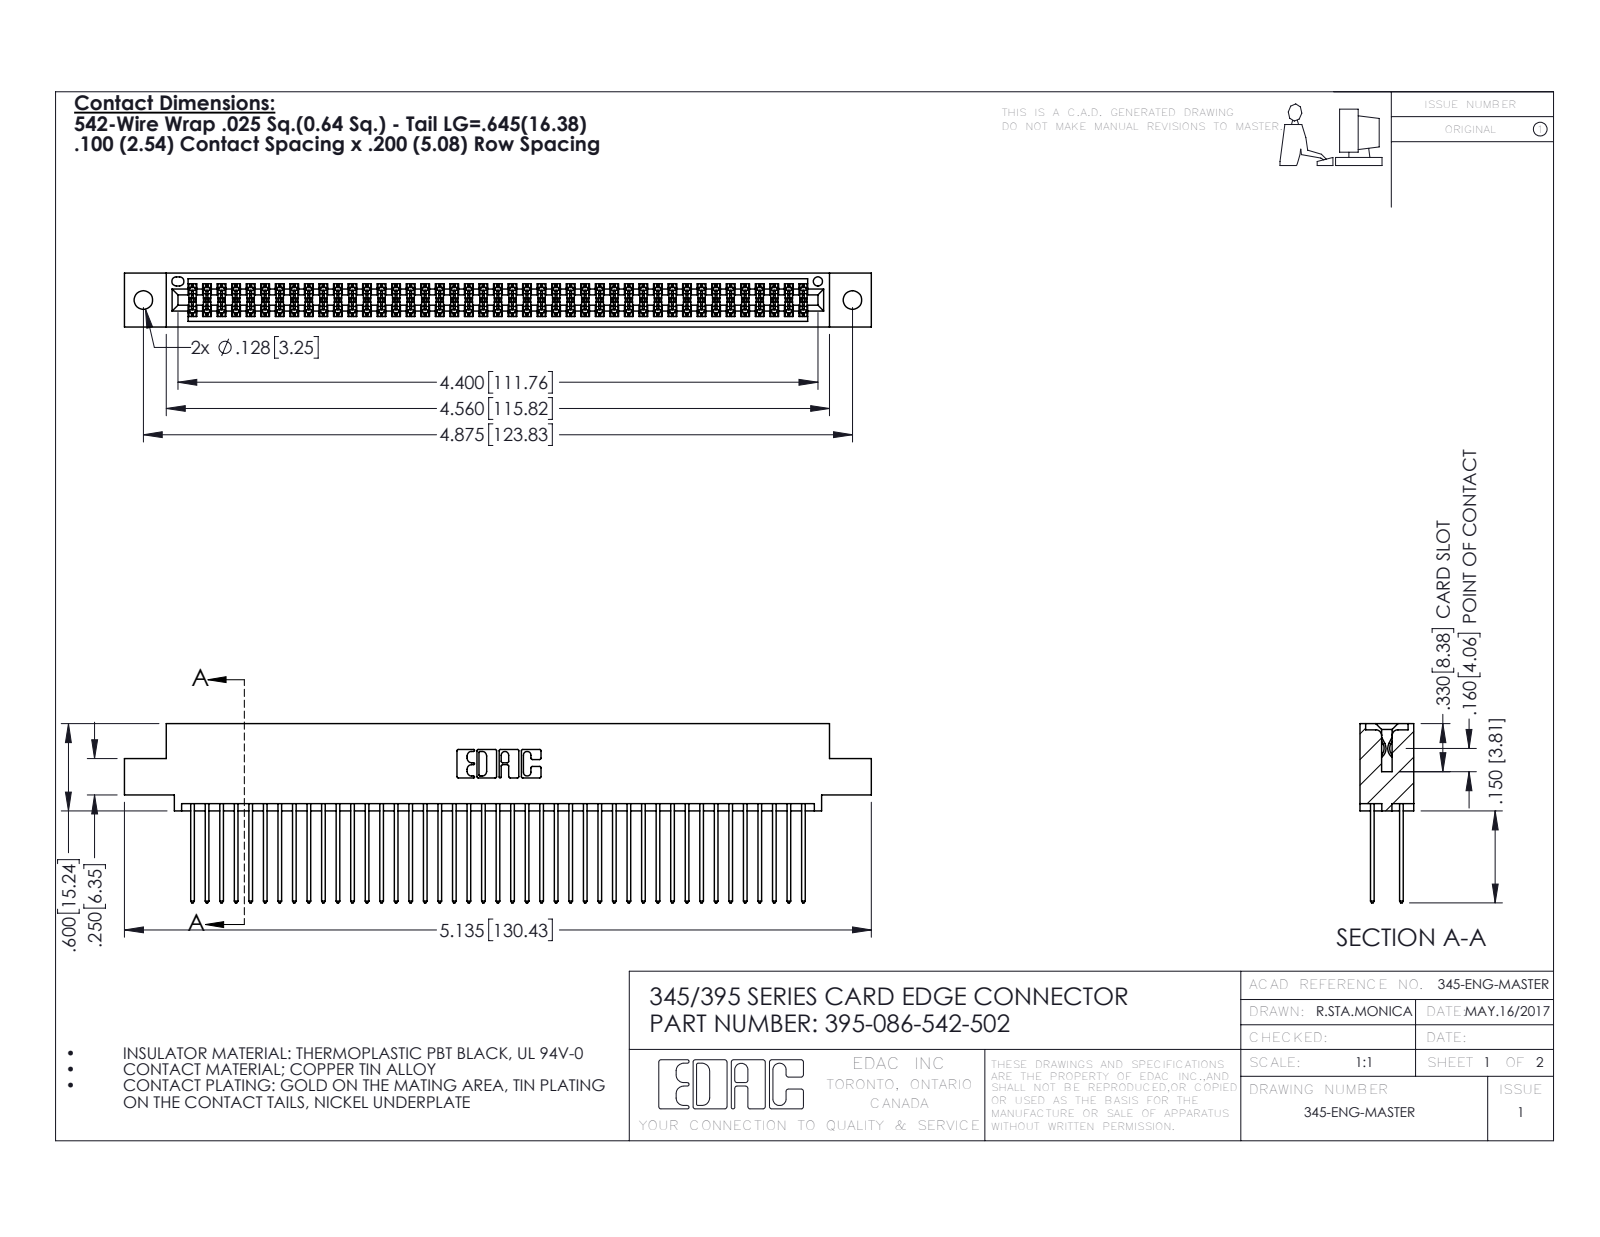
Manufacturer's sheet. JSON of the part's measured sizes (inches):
{"part_name": "345-292-001_345-293-142; 395-086-542-502; 345 Part_0.110 Offset - 0.128 Dia", "step_written_by": "SolidWorks 2016 (CONFIG_CONTROL_DESIGN)", "units": "inches", "bodies": {"solids": 87, "faces": 4430, "planar": 2922, "cylindrical": 1508, "other": 0}, "overall_size": [5.135, 1.232, 0.37], "volume_in3": 0.791, "surface_area_in2": 32.37, "round_holes": [[0.128, 2], [0.064, 1]], "partial_cylinders_radius": [[0.006, 129], [0.01, 86], [0.01, 22], [0.007, 6], [0.031, 6], [0.026, 3], [0.014, 2], [0.019, 2]], "face_to_face_distances": [0.298, 0.072, 0.2, 0.098, 0.272, 0.025, 0.225, 0.37, 0.175, 0.149], "hole_center_spacings": [0.27, 4.639, 4.875]}
